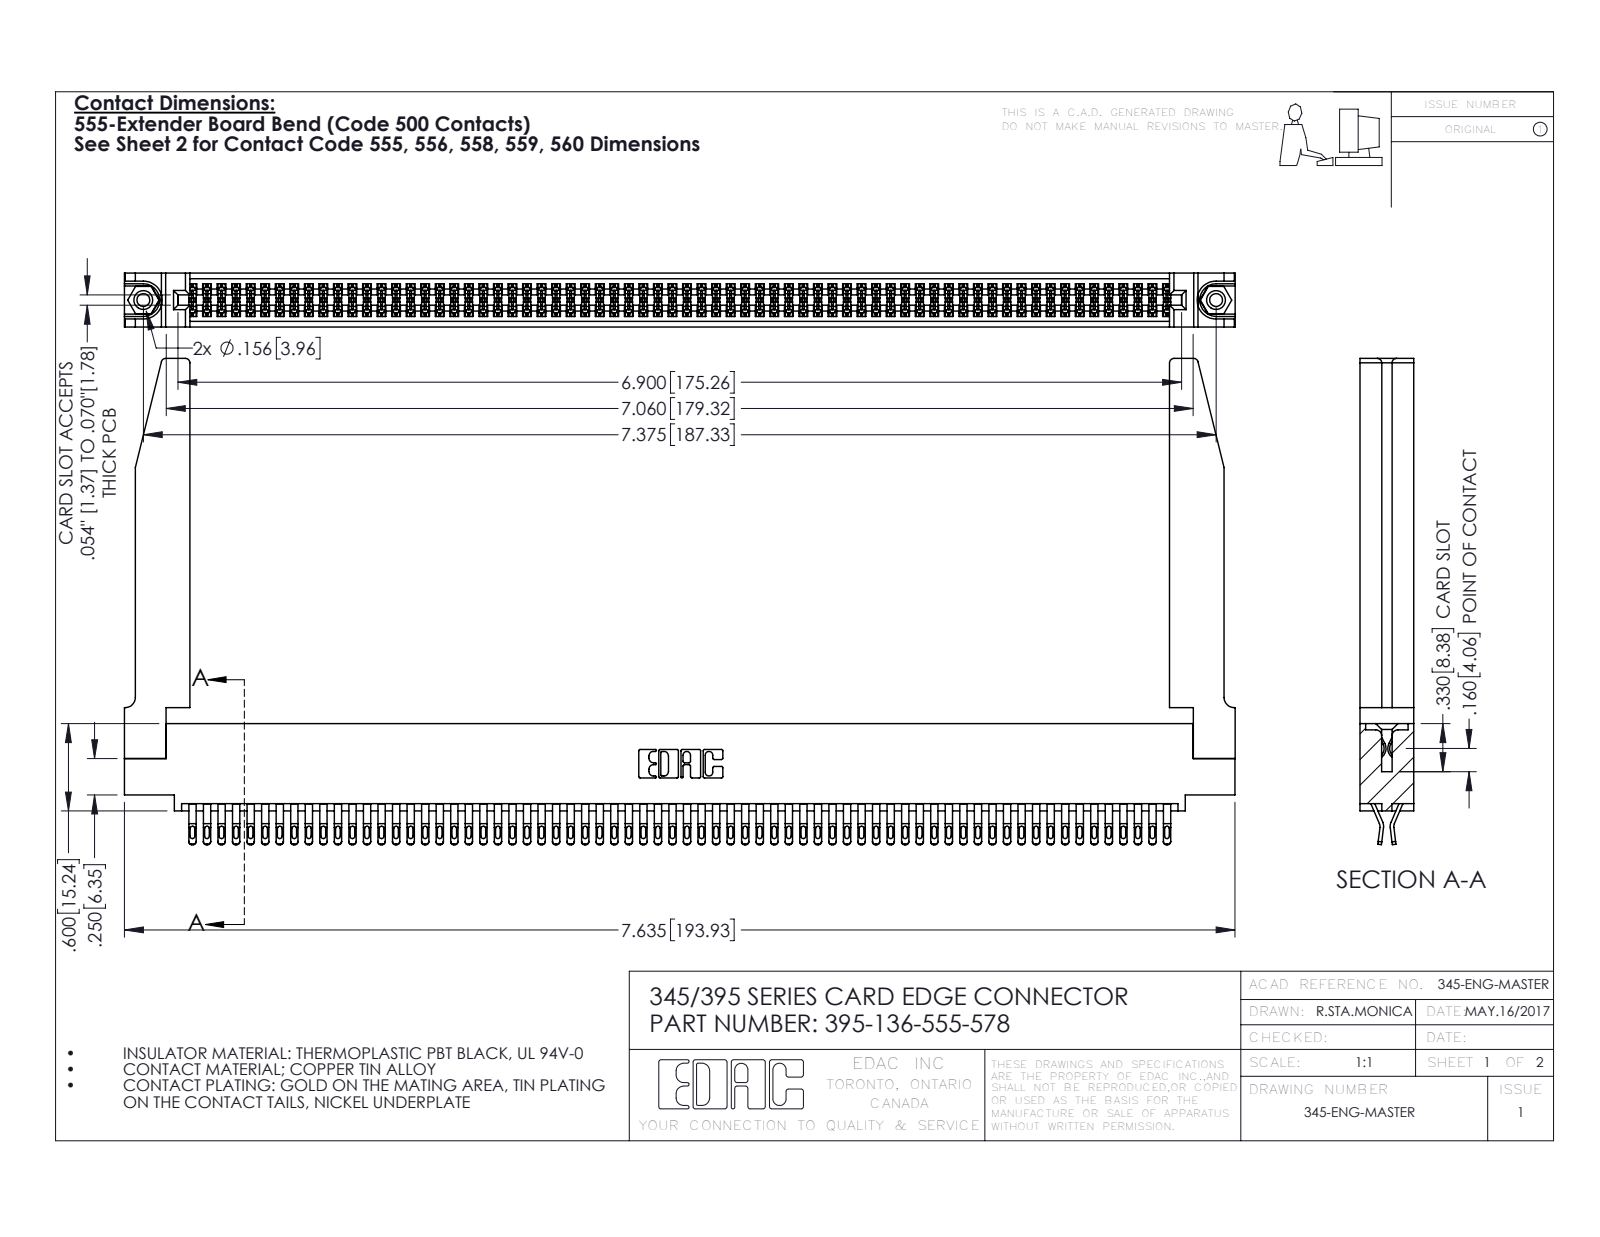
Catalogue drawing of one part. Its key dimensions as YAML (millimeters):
part_name: "345-220-078_345-220-078; 345-250-001_345-250-001-102; 395-136-555-578; 345-292-001_555 Tail (+1 more)"
step_written_by: "SolidWorks 2016 (CONFIG_CONTROL_DESIGN)"
units: millimeters
bodies: {solids: 141, faces: 7980, planar: 4442, cylindrical: 3486, other: 52}
overall_size: [194, 84.9, 9.4]
volume: 27170
surface_area: 37490
round_holes:
  - {diameter: 2.3, count: 2}
  - {diameter: 3.2, count: 2}
  - {diameter: 4, count: 2}
  - {diameter: 1.6, count: 1}
round_bosses_or_shafts:
  - {diameter: 3.9, count: 2}
partial_cylinders:
  - {radius: 0.4, count: 340}
  - {radius: 0.5, count: 272}
  - {radius: 0.2, count: 204}
  - {radius: 0.3, count: 22}
  - {radius: 0.8, count: 8}
  - {radius: 0.2, count: 6}
  - {radius: 0.8, count: 6}
  - {radius: 0.7, count: 3}
face_to_face_distances: [1.8, 7.6, 9.4, 0.6, 2.5, 6.9, 5.1, 5.7, 4.4, 3.8]
hole_center_spacings: [6.9, 181.3, 187.3]
